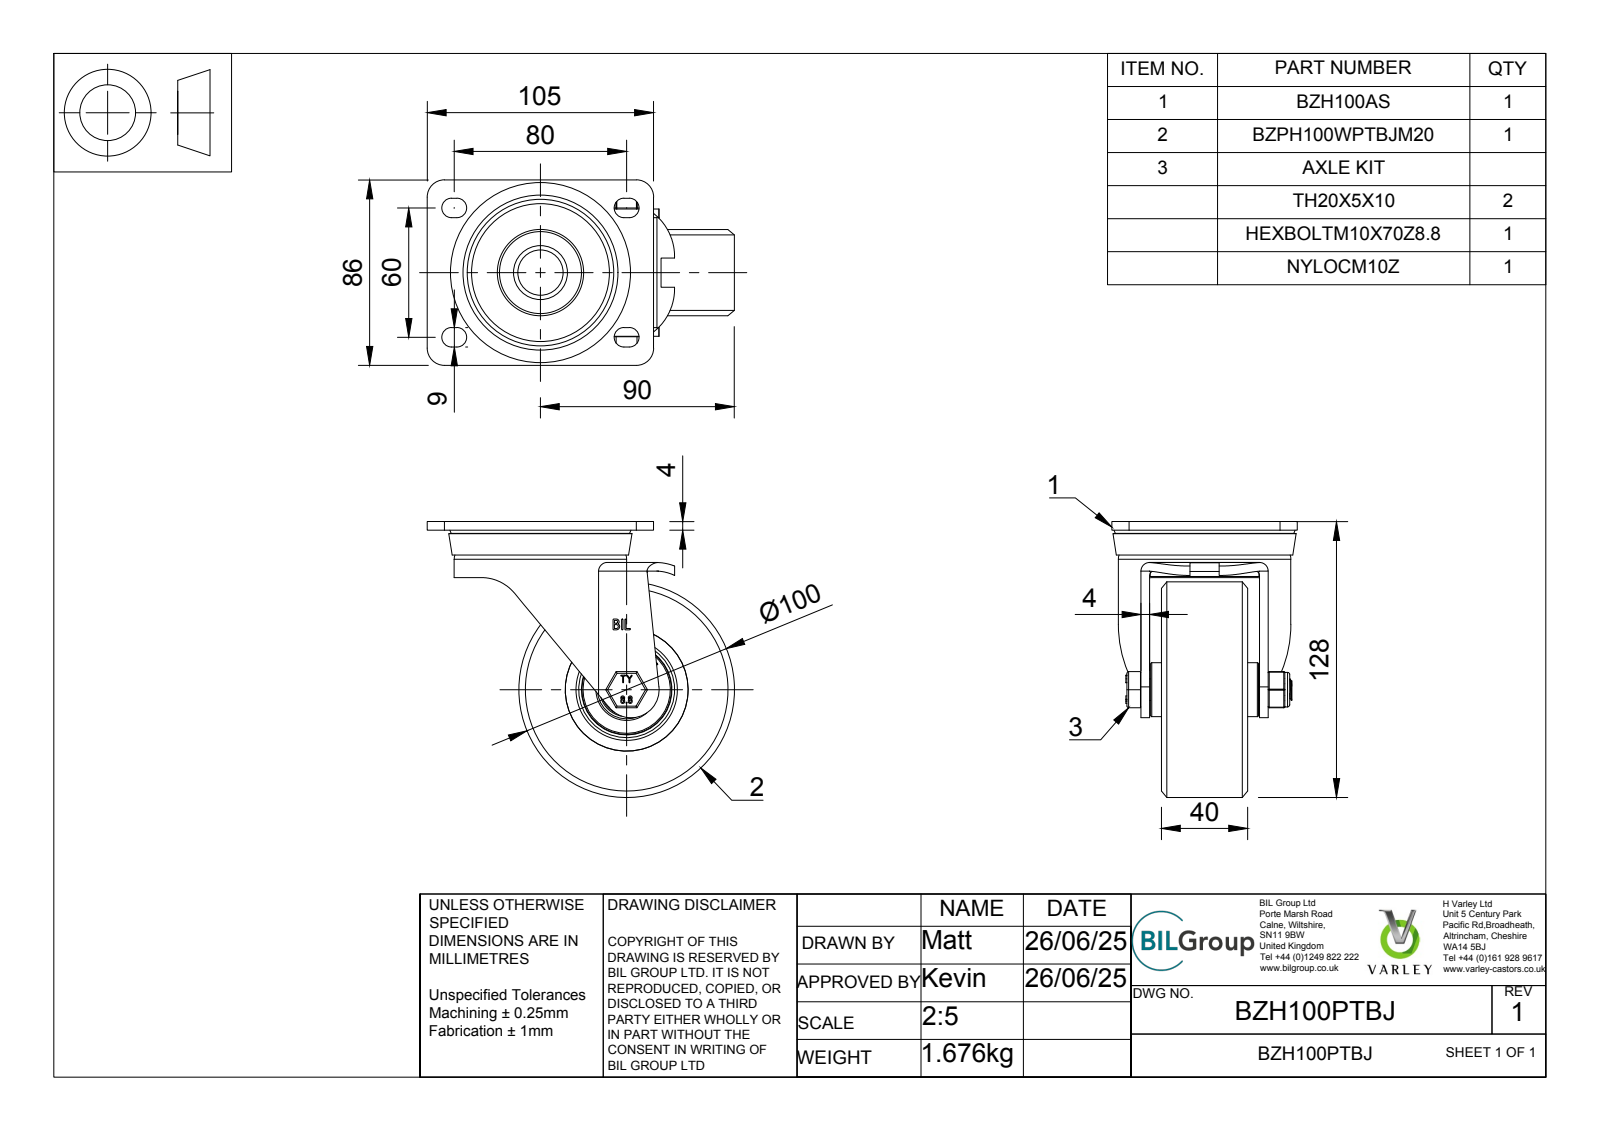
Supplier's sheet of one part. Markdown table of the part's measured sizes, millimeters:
| quantity | value |
| --- | --- |
| part name | BZH100PTBJ v4; BZH100AS - 2 v1; ZINC PLATED, PRESSED STEEL TOP PLATE (1); ZINC PLATED, PRESSED STEEL FORKS (1) (+8 more) |
| STEP written by | Autodesk Translation Framework v14.10.0.0 (AUTOMOTIVE_DESIGN) |
| units | millimeters |
| bodies | 37 solids, 1342 faces (631 planar, 270 cylindrical, 441 other) |
| overall size | 142.5 × 128 × 86 |
| volume | 429 583 mm³ |
| surface area | 153 727 mm² |
| round holes (diameter × count) | 10 × 1, 10.2 × 1, 10.5 × 1, 12 × 1, 20 × 1, 25 × 1, 28.5 × 1, 30 × 1, 32 × 1, 41.5 × 1, 42 × 1, 44 × 1 |
| round bosses / shafts (diameter × count) | 100 × 1, 80 × 1, 50.5 × 1, 40.5 × 1, 40 × 1, 31 × 1, 29 × 1, 27 × 1 |
| partial cylindrical surfaces (radius × count) | 0.5 × 18, 4 × 14, 6 × 12, 4.5 × 8, 0.75 × 6, 2 × 4, 8 × 4, 25.41 × 2 |
| main face-to-face distances | 4, 26, 40, 5.5, 14, 13.5, 11.5, 19.5, 7.5, 19 |
